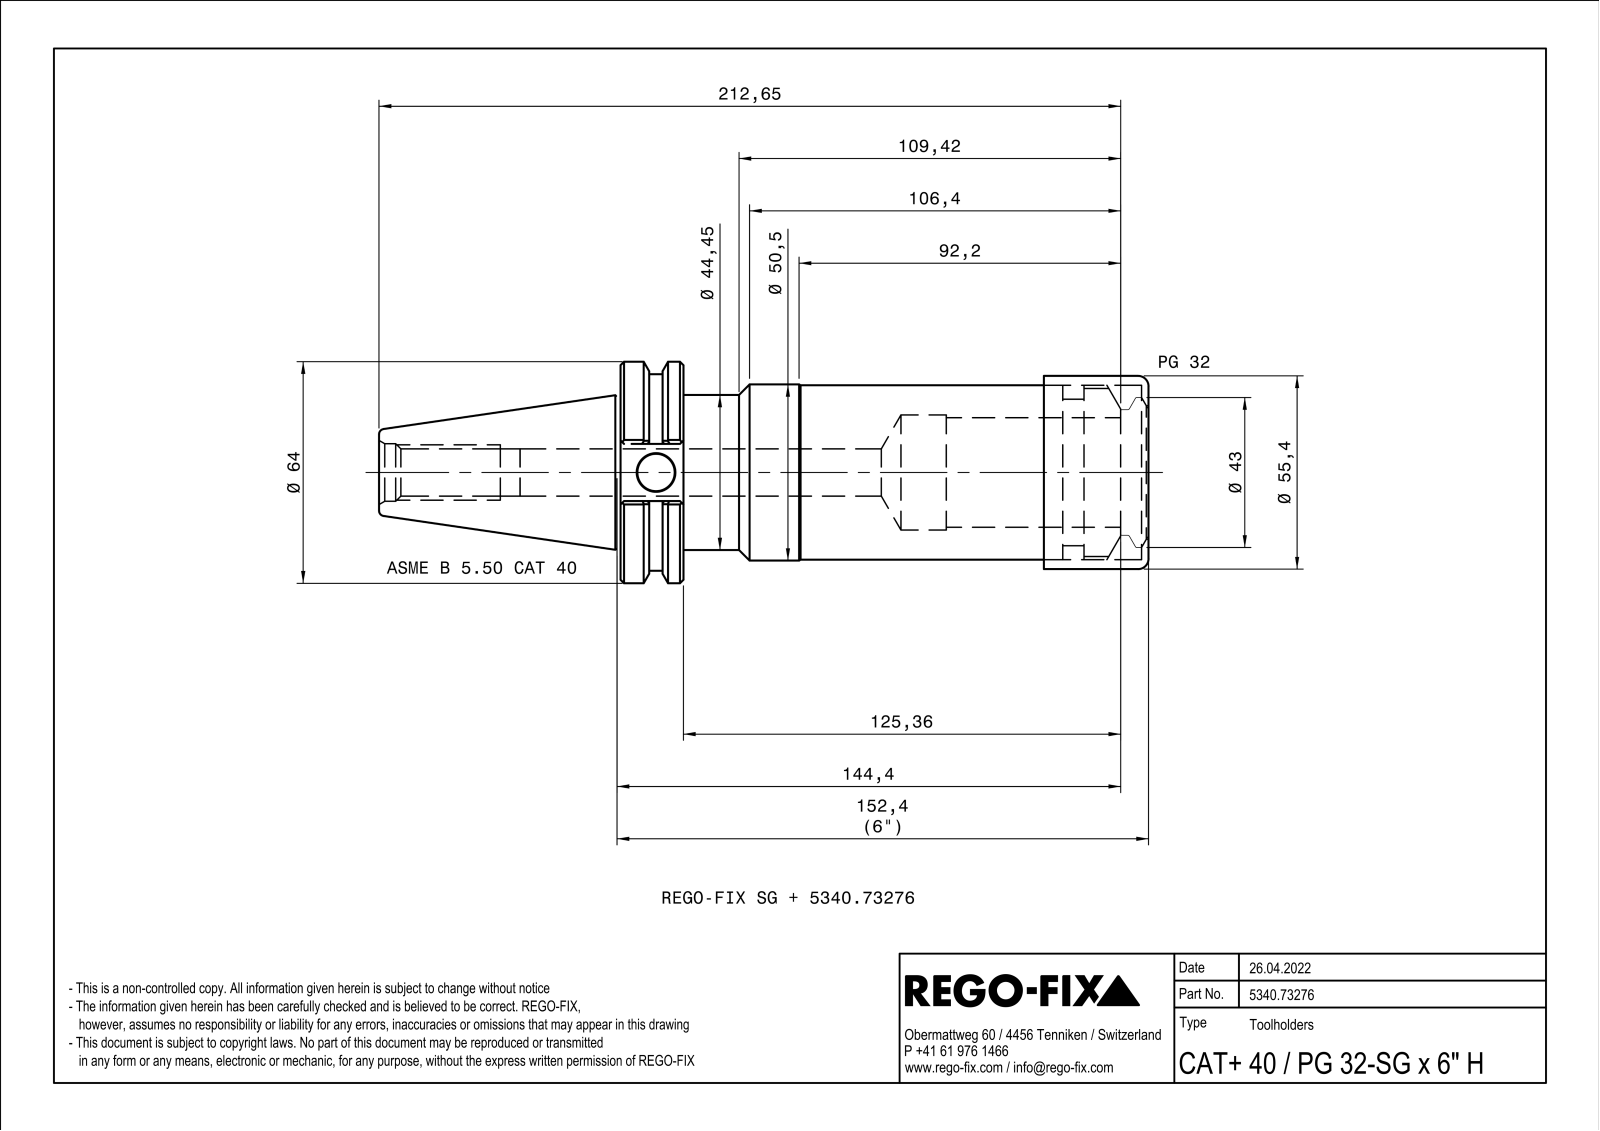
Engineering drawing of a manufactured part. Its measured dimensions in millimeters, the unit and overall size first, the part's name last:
Units: millimetres
Overall size (bounding box): 220.65 × 63.5 × 60.82
Round holes (diameter × count): ⌀12 ×1, ⌀13.3 ×1, ⌀13.38 ×1, ⌀16.5 ×1, ⌀33 ×1, ⌀38.25 ×1, ⌀48.38 ×1, ⌀50.05 ×1, ⌀51 ×1
Round bosses / shafts (diameter × count): ⌀63.5 ×1, ⌀56.36 ×1, ⌀55.4 ×1, ⌀55 ×1, ⌀50.5 ×1, ⌀50 ×1, ⌀44.45 ×1, ⌀43.85 ×1
Partial cylindrical surfaces — rounded edges, fillets, slot ends (radius × count): R0.5 ×4
Main face-to-face distances: 18.05, 133.35, 151.4, 24.6, 108.75, 126.8, 18.5, 6.1, 114.85, 132.9
Volume: 287 265 mm³ · Surface area: 59 290 mm²
Bodies: 1 solid, 109 faces (38 planar, 27 cylindrical, 44 other)
Part name (STEP PRODUCT): NOCUT
STEP written by: SIEMENS PLM Software Solid Edge ST10 (AUTOMOTIVE_DESIGN)
